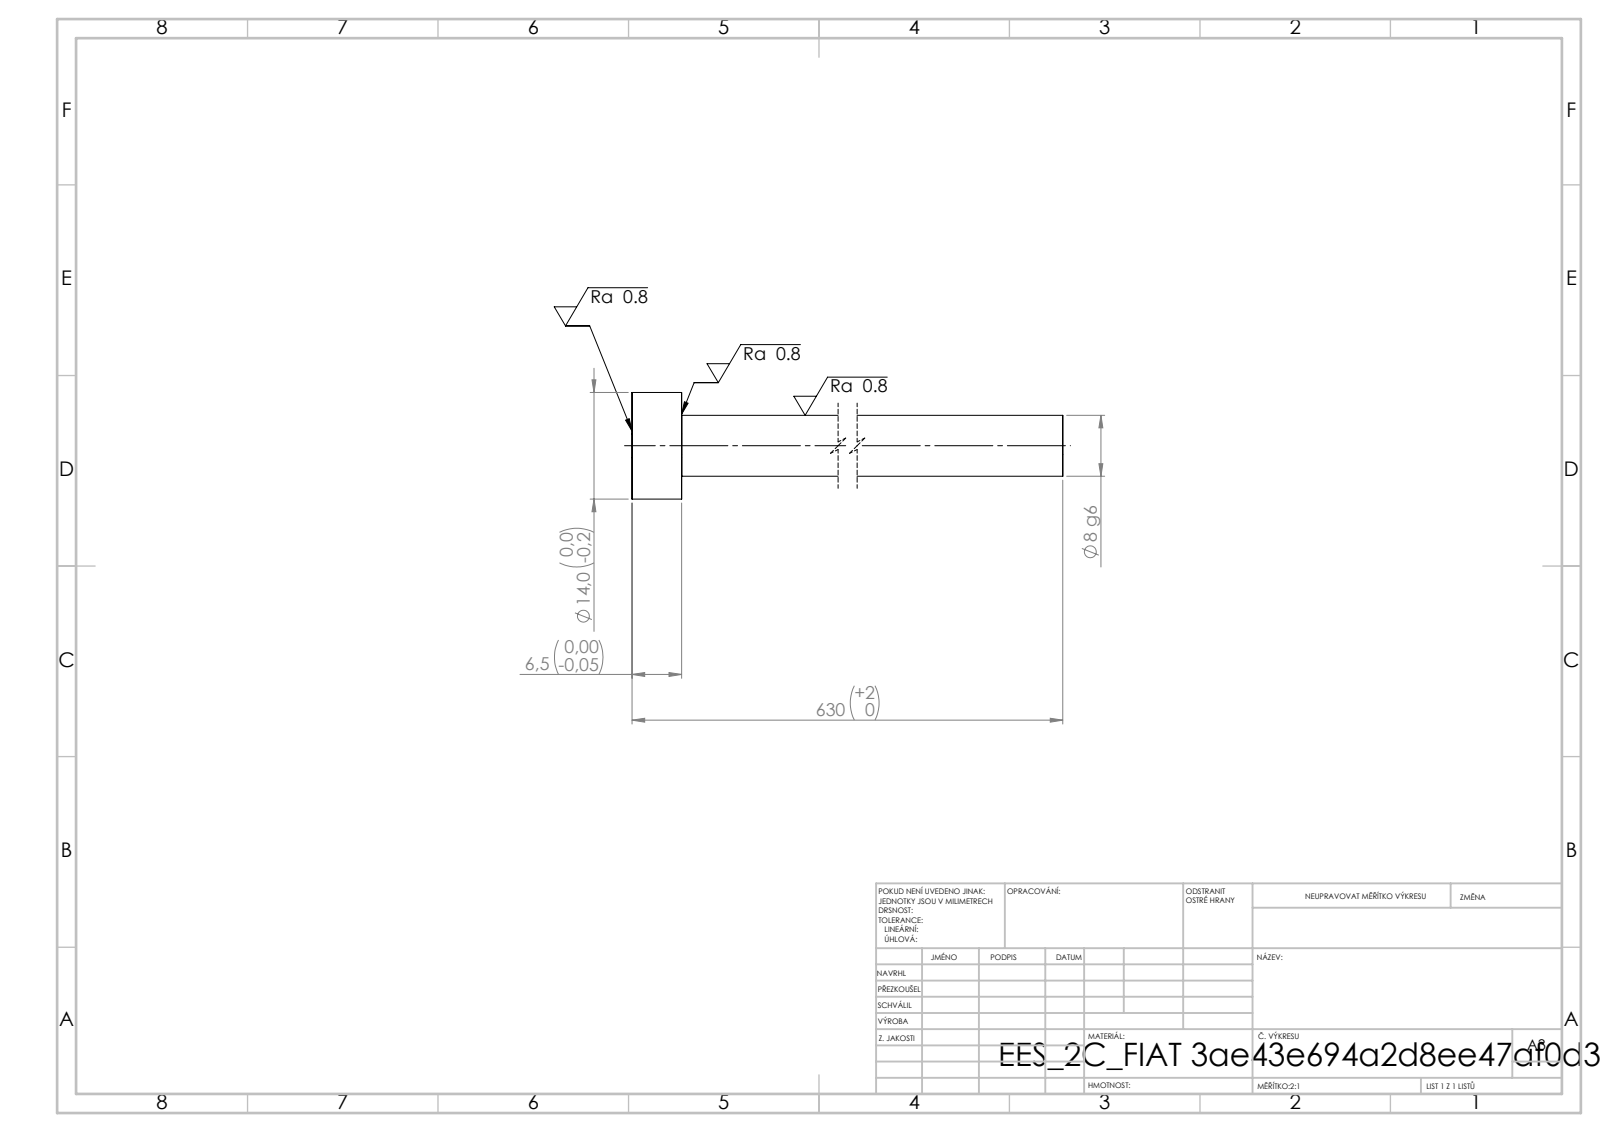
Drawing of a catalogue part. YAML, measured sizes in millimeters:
step_written_by: "SolidWorks 2019 (CONFIG_CONTROL_DESIGN)"
units: millimeters
bodies: {solids: 1, faces: 7, planar: 3, cylindrical: 4, other: 0}
overall_size: [630, 14, 14]
volume: 32341
surface_area: 16264
round_bosses_or_shafts:
  - {diameter: 14, count: 1}
  - {diameter: 8, count: 1}
face_to_face_distances: [6.5, 630, 623.5]
